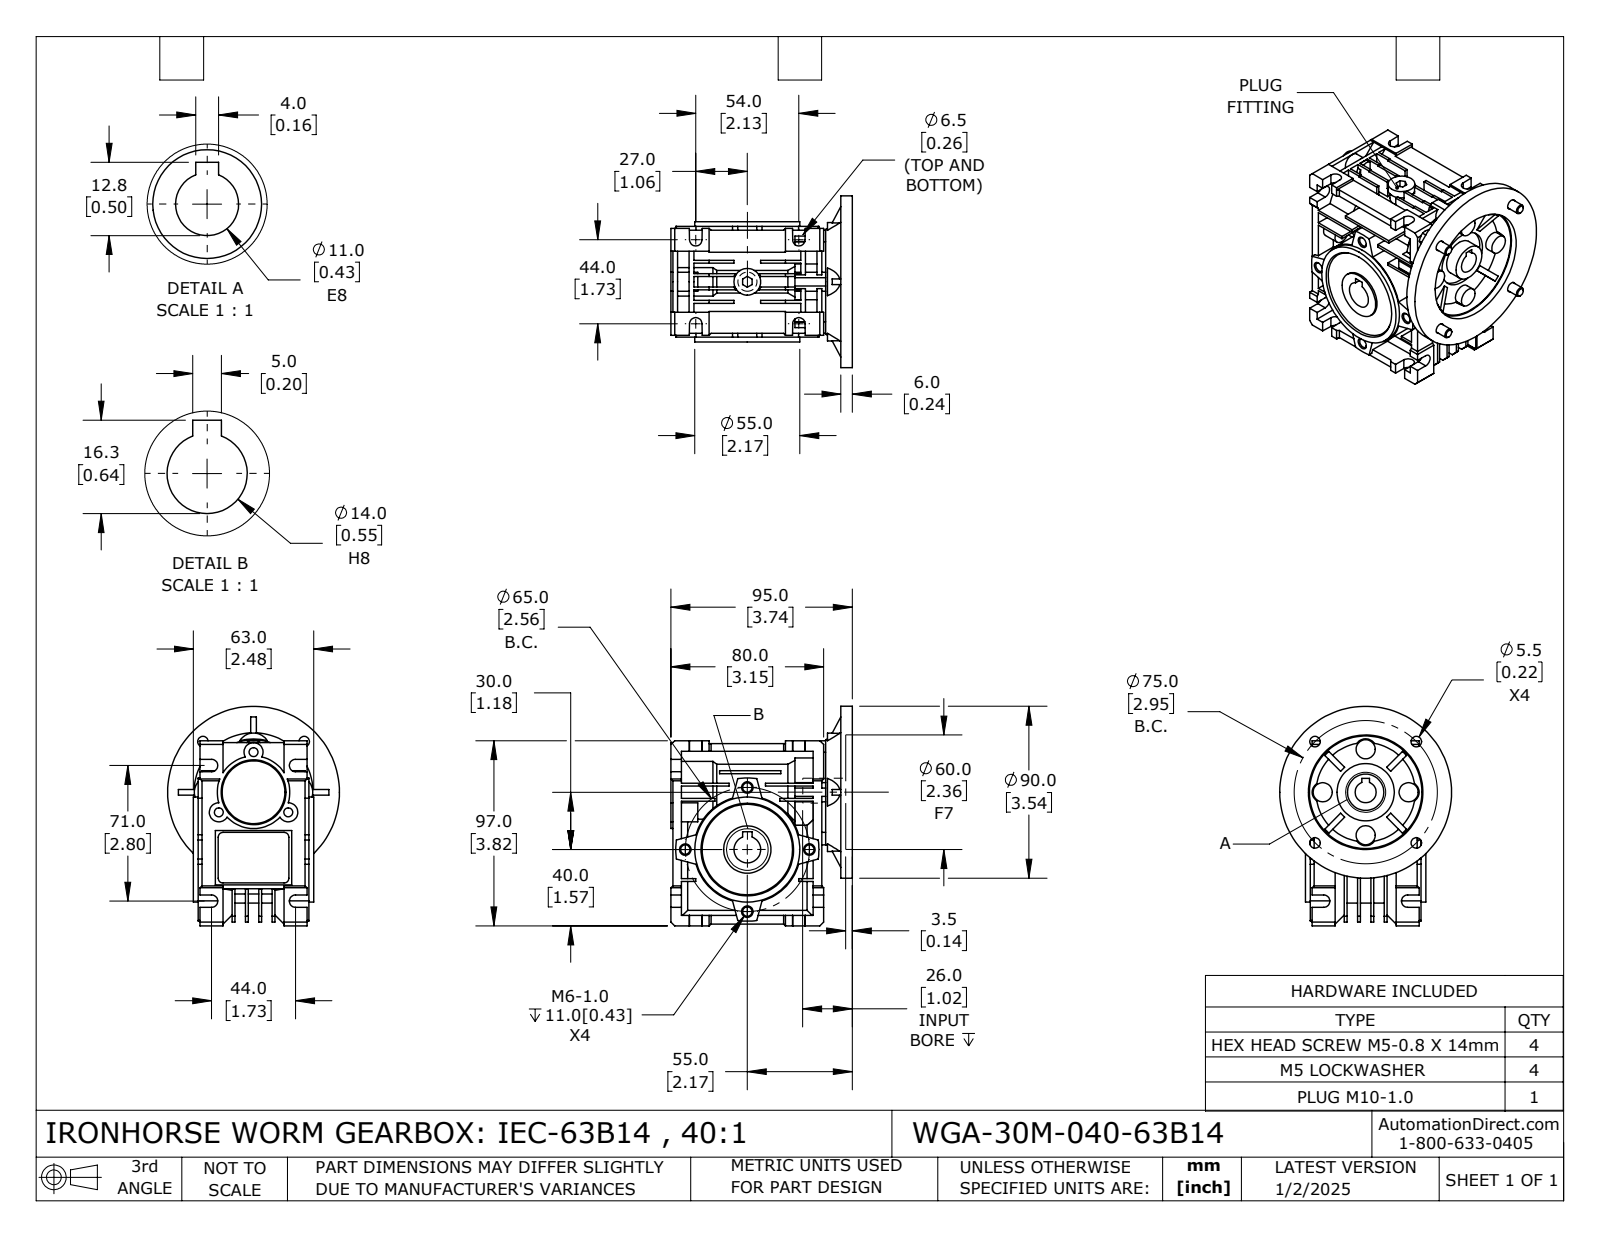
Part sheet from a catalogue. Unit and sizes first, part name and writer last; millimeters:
Units: millimetres
Overall size (bounding box): 115 × 101.7 × 90
Round holes (diameter × count): ⌀4.92 ×4, ⌀5.1 ×4, ⌀5.5 ×4, ⌀4.65 ×3, ⌀4.92 ×2, ⌀9 ×1, ⌀11 ×1, ⌀11.5 ×1, ⌀14 ×1, ⌀14.5 ×1, ⌀19 ×1, ⌀24.8 ×1
Round bosses / shafts (diameter × count): ⌀10 ×4, ⌀9.2 ×4, ⌀5 ×4, ⌀90 ×1, ⌀56 ×1, ⌀55 ×1, ⌀38 ×1, ⌀37 ×1
Partial cylindrical surfaces — rounded edges, fillets, slot ends (radius × count): R3.25 ×8, R2.5 ×4, R5.5 ×4, R8.5 ×4, R5 ×3, R7.5 ×1, R17 ×1, R21.5 ×1
Main face-to-face distances: 1.5, 7, 5.5, 1, 14, 4.5, 8.5, 6, 10, 2
Hole centre spacings: 32.5, 37.5, 45.96, 53.04, 21, 18.06, 27.09, 36.37
Volume: 339 639 mm³ · Surface area: 112 960 mm²
Bodies: 14 solids, 905 faces (566 planar, 239 cylindrical, 100 other)
Part name (STEP PRODUCT): WGA-30M-040-63B14
STEP written by: SolidWorks 2024 (CONFIG_CONTROL_DESIGN)
